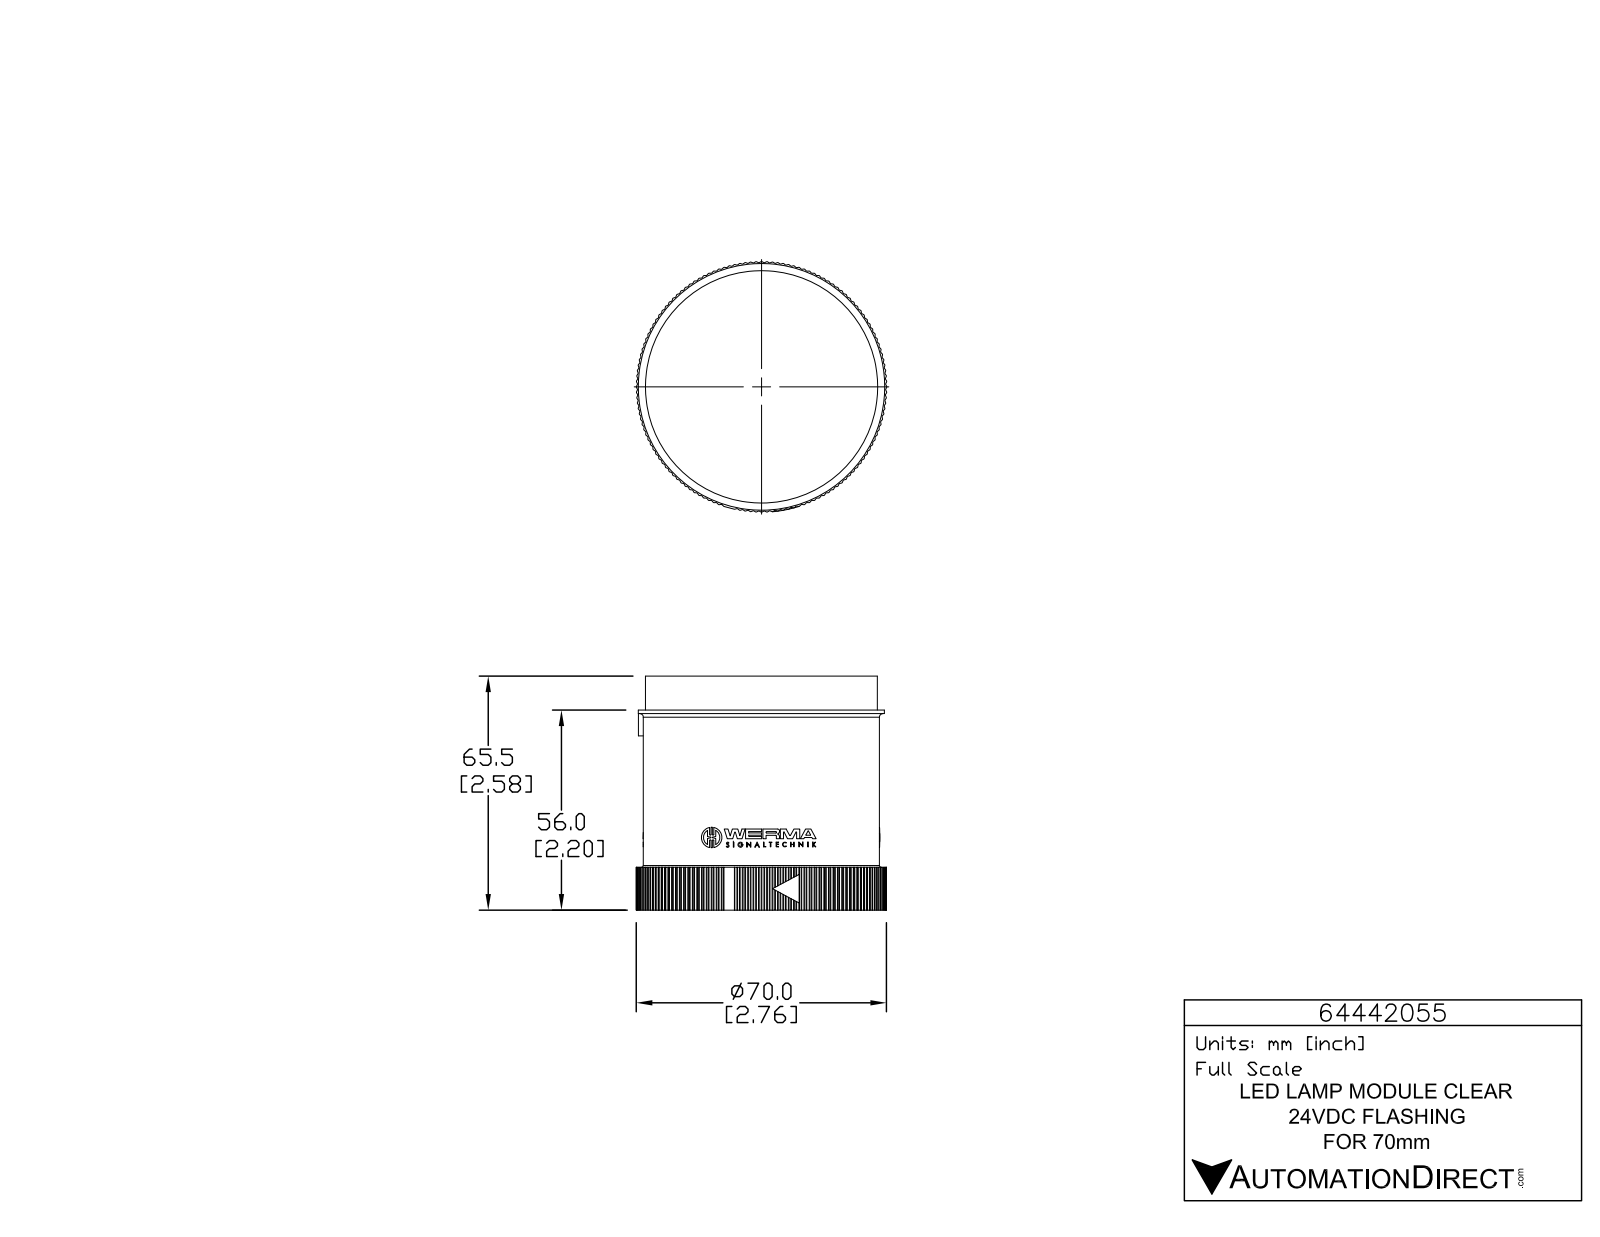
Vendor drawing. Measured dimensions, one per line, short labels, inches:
name: 64442055
written by: SolidWorks 2015 (AUTOMOTIVE_DESIGN)
unit: in
bodies: 1 solid, 1400 faces (832 planar, 563 cylindrical, 5 other)
size: 2.762 × 2.762 × 2.579
volume: 12.02 in³; area: 37.48 in²
holes: 3× ⌀0.039, 1× ⌀2.575
bosses: 3× ⌀0.226, 3× ⌀0.056, 1× ⌀2.717, 1× ⌀2.606, 1× ⌀2.559
rounds: 285× R0.008, 6× R0.008, 6× R0.008, 6× R0.008, 6× R0.131, 3× R0.004, 3× R0.005, 3× R0.008
face distances: 2.201, 2.451, 0.378, 2.579, 2.205, 1.827, 0.374, 2.452, 0.472, 0.094
